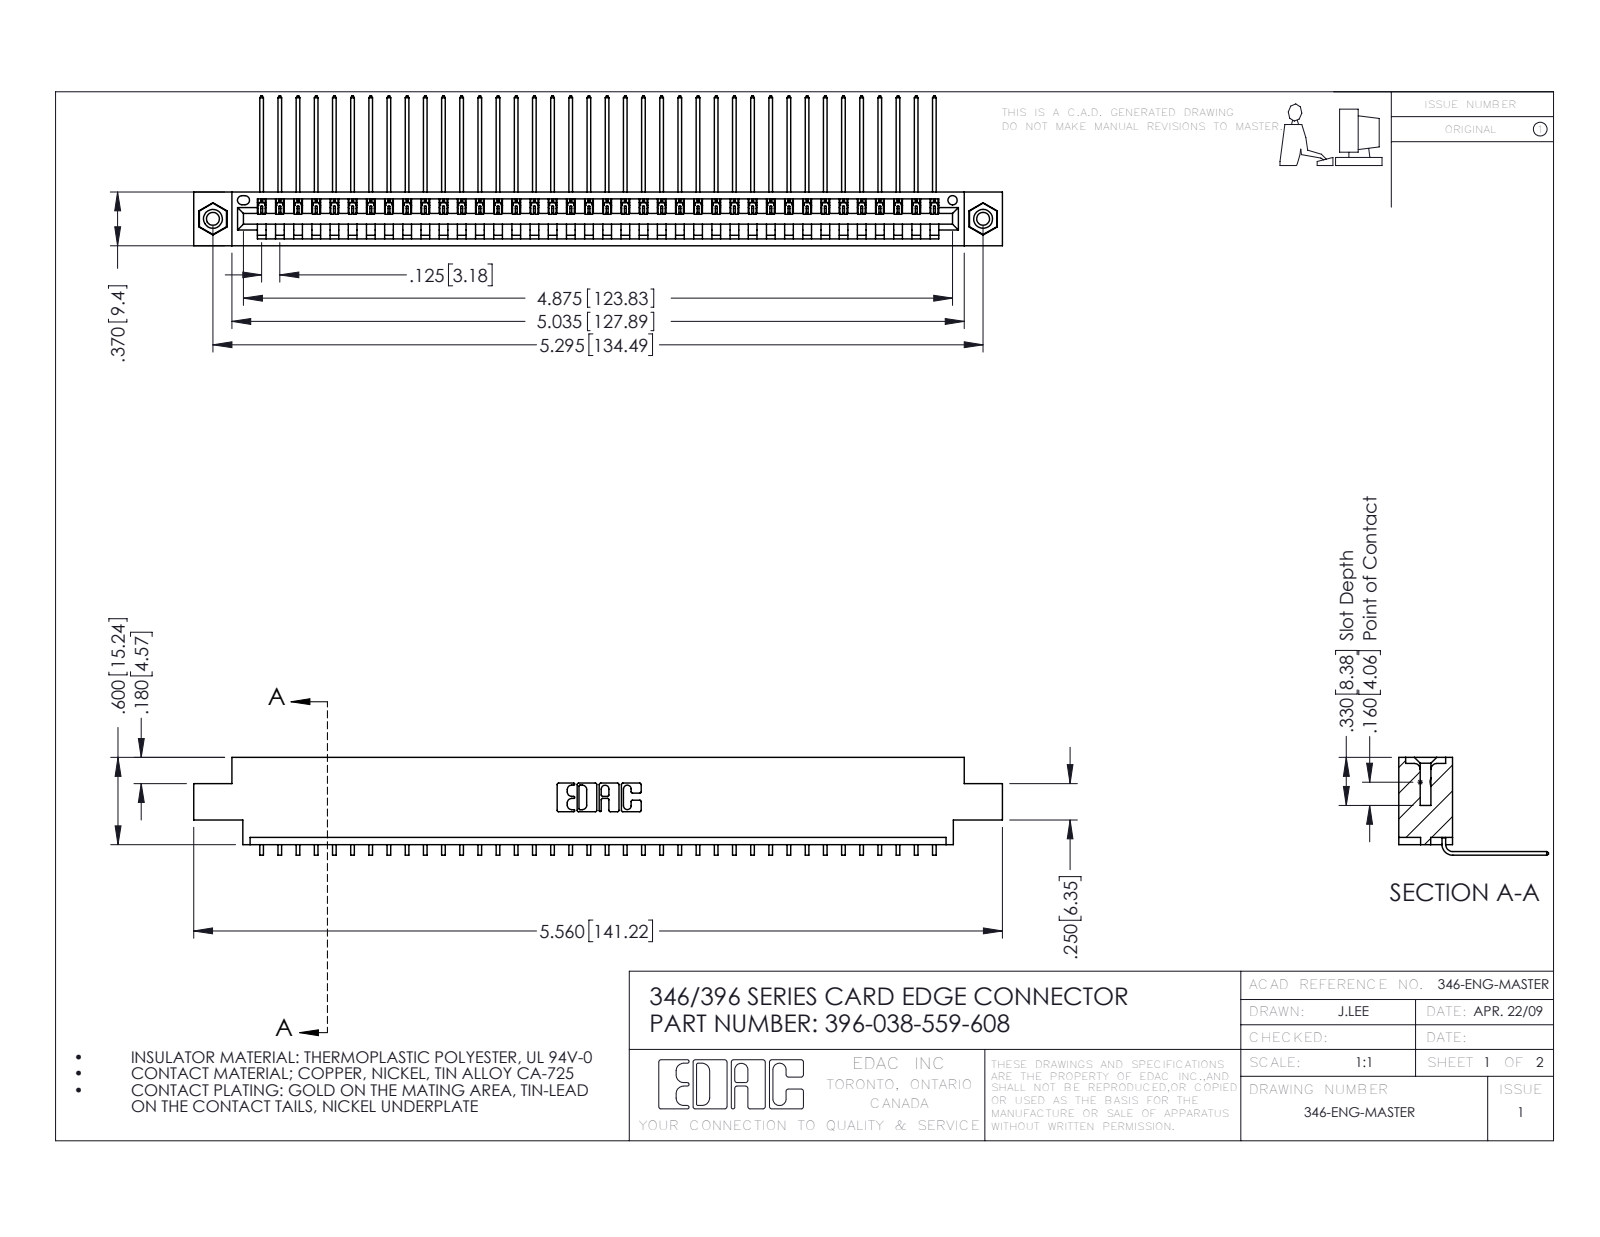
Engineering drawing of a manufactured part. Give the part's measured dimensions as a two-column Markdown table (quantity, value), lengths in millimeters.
| quantity | value |
| --- | --- |
| part name | 345-250-001_345-250-003-102; 346 Part_0.170 Offset - 0.156 Dia-TI; 396-038-559-608; 345-292-001_558 559 Tail - 1 |
| STEP written by | SolidWorks 2016 (CONFIG_CONTROL_DESIGN) |
| units | millimeters |
| bodies | 41 solids, 2466 faces (1708 planar, 742 cylindrical, 16 other) |
| overall size | 141.2 × 26.2 × 17.1 |
| volume | 13 500 mm³ |
| surface area | 17 710 mm² |
| round holes (diameter × count) | 2.3 × 2, 3.2 × 2, 4 × 2, 1.6 × 1 |
| round bosses / shafts (diameter × count) | 3.9 × 2 |
| partial cylindrical surfaces (radius × count) | 0.2 × 76, 0.3 × 22, 0.2 × 6, 0.8 × 6, 0.7 × 3, 0.8 × 2, 1 × 2, 0.4 × 1 |
| main face-to-face distances | 1.2, 8.2, 9.4, 0.6, 6.4, 1.8, 5.6, 3.8, 7.6, 2.5 |
| hole center spacings | 6.2, 129.2, 134.5 |
